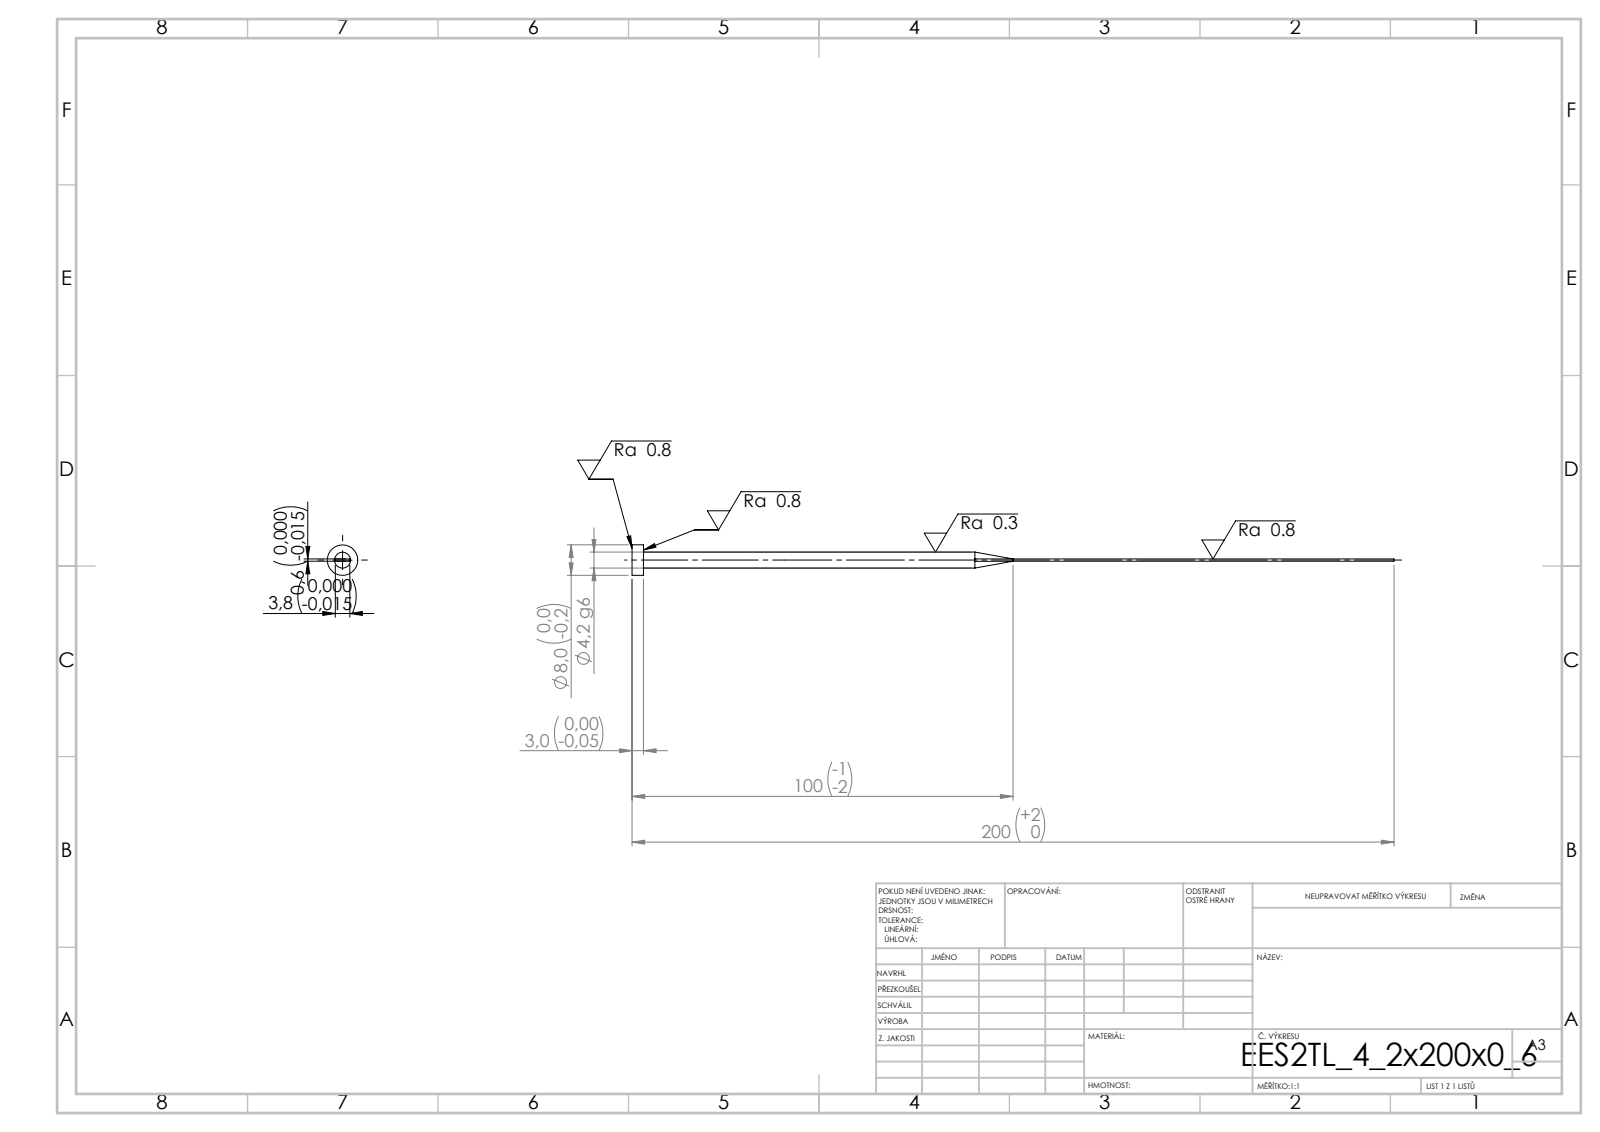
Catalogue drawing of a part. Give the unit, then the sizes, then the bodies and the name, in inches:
Units: inches
Overall size (bounding box): 7.874 × 0.315 × 0.315
Round bosses / shafts (diameter × count): ⌀0.315 ×1, ⌀0.165 ×1
Main face-to-face distances: 0.024, 0.15, 0.118, 7.874, 7.756
Volume: 0.101 in³ · Surface area: 3.562 in²
Bodies: 1 solid, 15 faces (7 planar, 4 cylindrical, 4 other)
STEP written by: SolidWorks 2019 (CONFIG_CONTROL_DESIGN)
